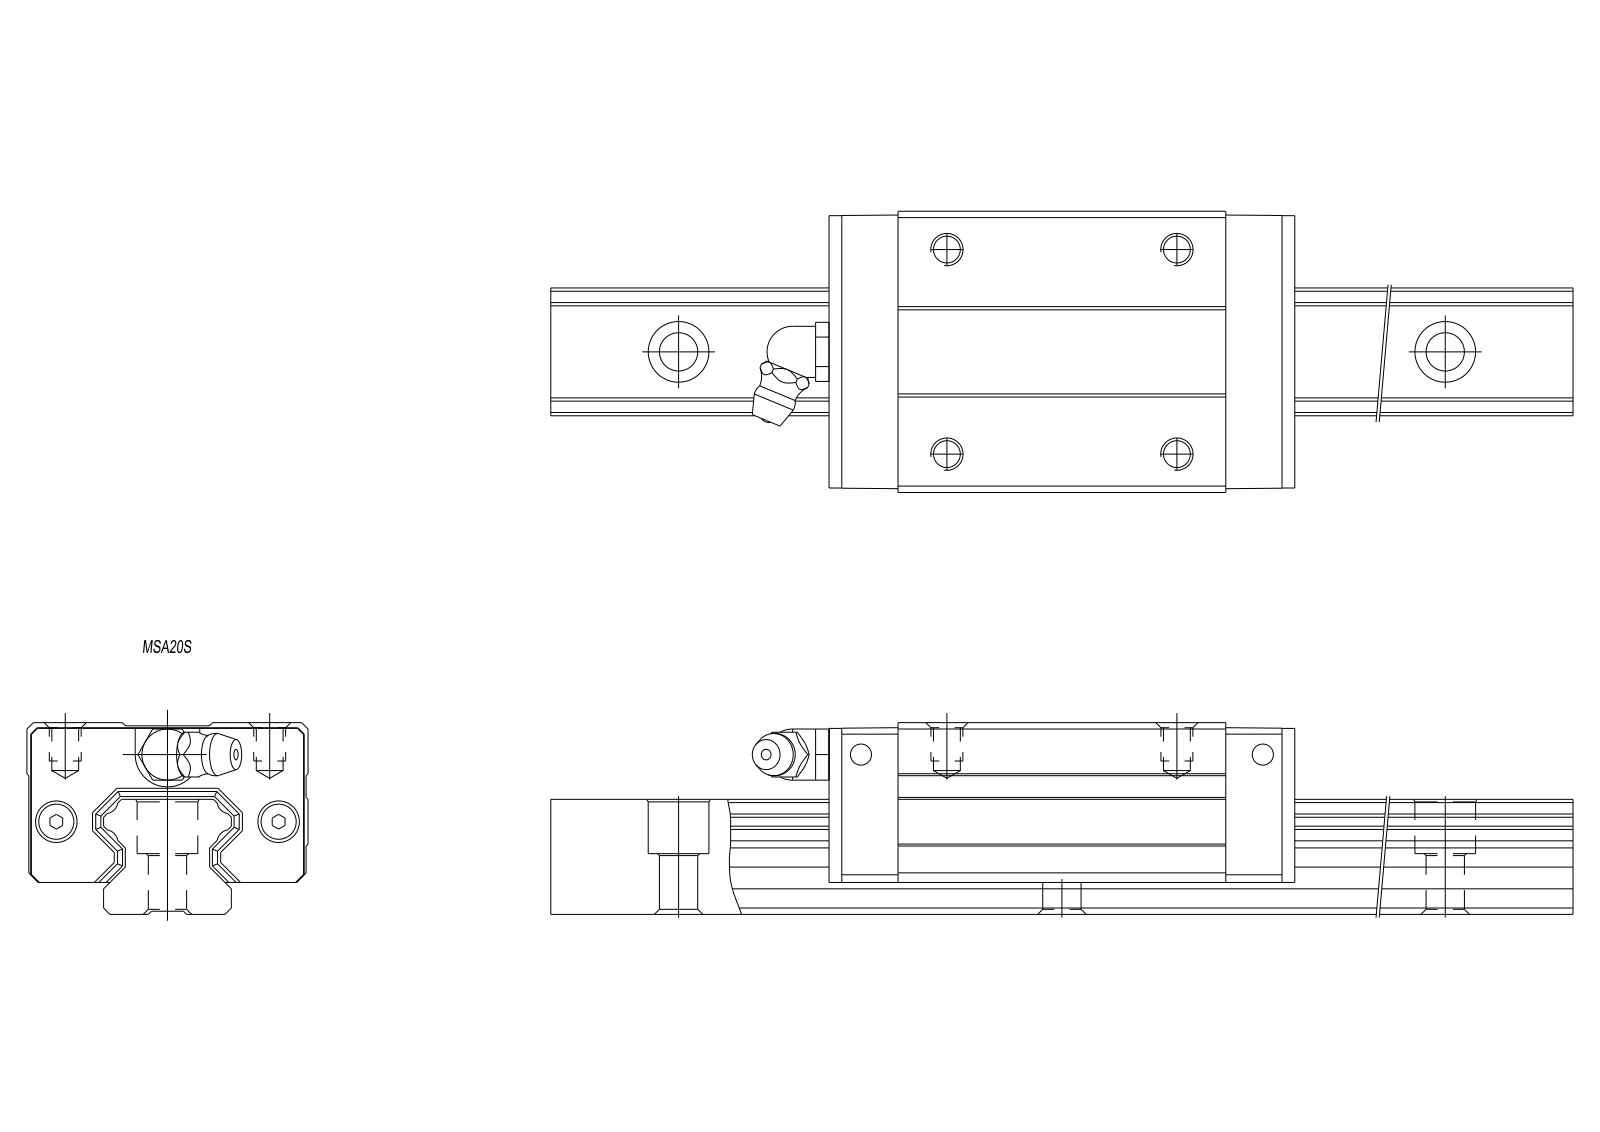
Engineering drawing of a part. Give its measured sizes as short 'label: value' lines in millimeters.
written by: Kubotek KeyCreator V6.5.2 (0407) (CONFIG_CONTROL_DESIGN)
unit: mm
bodies: 3 solids, 206 faces (135 planar, 54 cylindrical, 17 other)
size: 220 × 44 × 30
volume: 124 490 mm³; area: 34 566 mm²
holes: 4× ⌀5, 4× ⌀6, 4× ⌀9.5, 2× ⌀3.25, 2× ⌀6.5
bosses: 1× ⌀8
rounds: 4× R2.2, 1× R5.05
face distances: 18, 12, 0.5, 29.5, 5, 13, 0.4, 30, 25, 3.47
hole spacings: 20, 50.6, 73.76, 109.18, 60, 32, 36, 48.17
